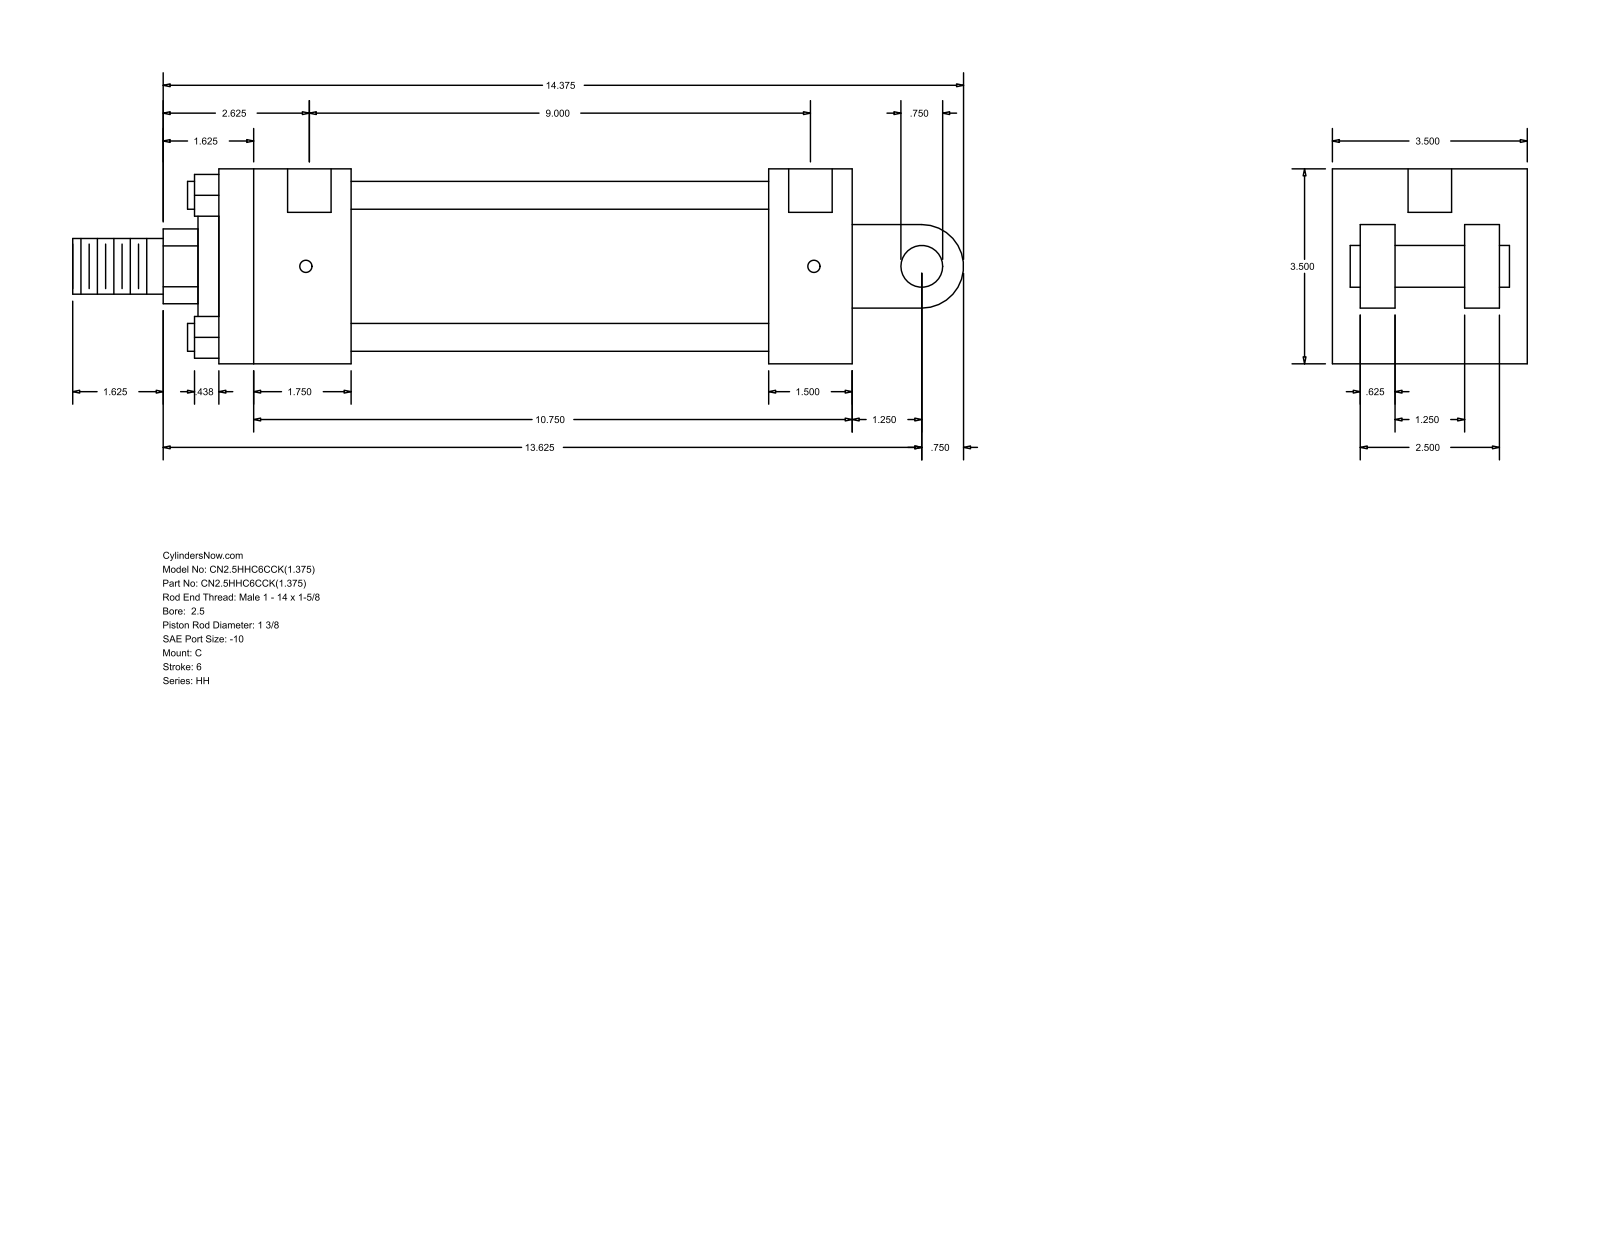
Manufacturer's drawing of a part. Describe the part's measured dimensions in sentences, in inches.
The part is named "HH_C__0250_1.375". Its 3-D file was written by "GSSL Pune (CONFIG_CONTROL_DESIGN)". It is 0 solids with 99 faces: 70 planar, 29 cylindrical and 0 other. Overall it measures 16 by 3.5 by 3.5 inches. Round holes: 4 of diameter 0.219, 2 of diameter 0.781. Round bosses or shafts: 4 of diameter 0.5, 1 of diameter 2.875, 1 of diameter 2, 1 of diameter 1.375, 1 of diameter 1, 1 of diameter 0.75. Partial cylindrical surfaces (rounded edges, fillets, slot ends): 1 of radius 0.672, 1 of radius 0.75. The main face-to-face distances are 3.5, 11.375, 2.5, 0.5, 9.875, 1.5, 2.375, 7.5, 9, 3. The hole center spacings are 9.125, 0.062, 0.063, 9, 9.062, 9.063.
